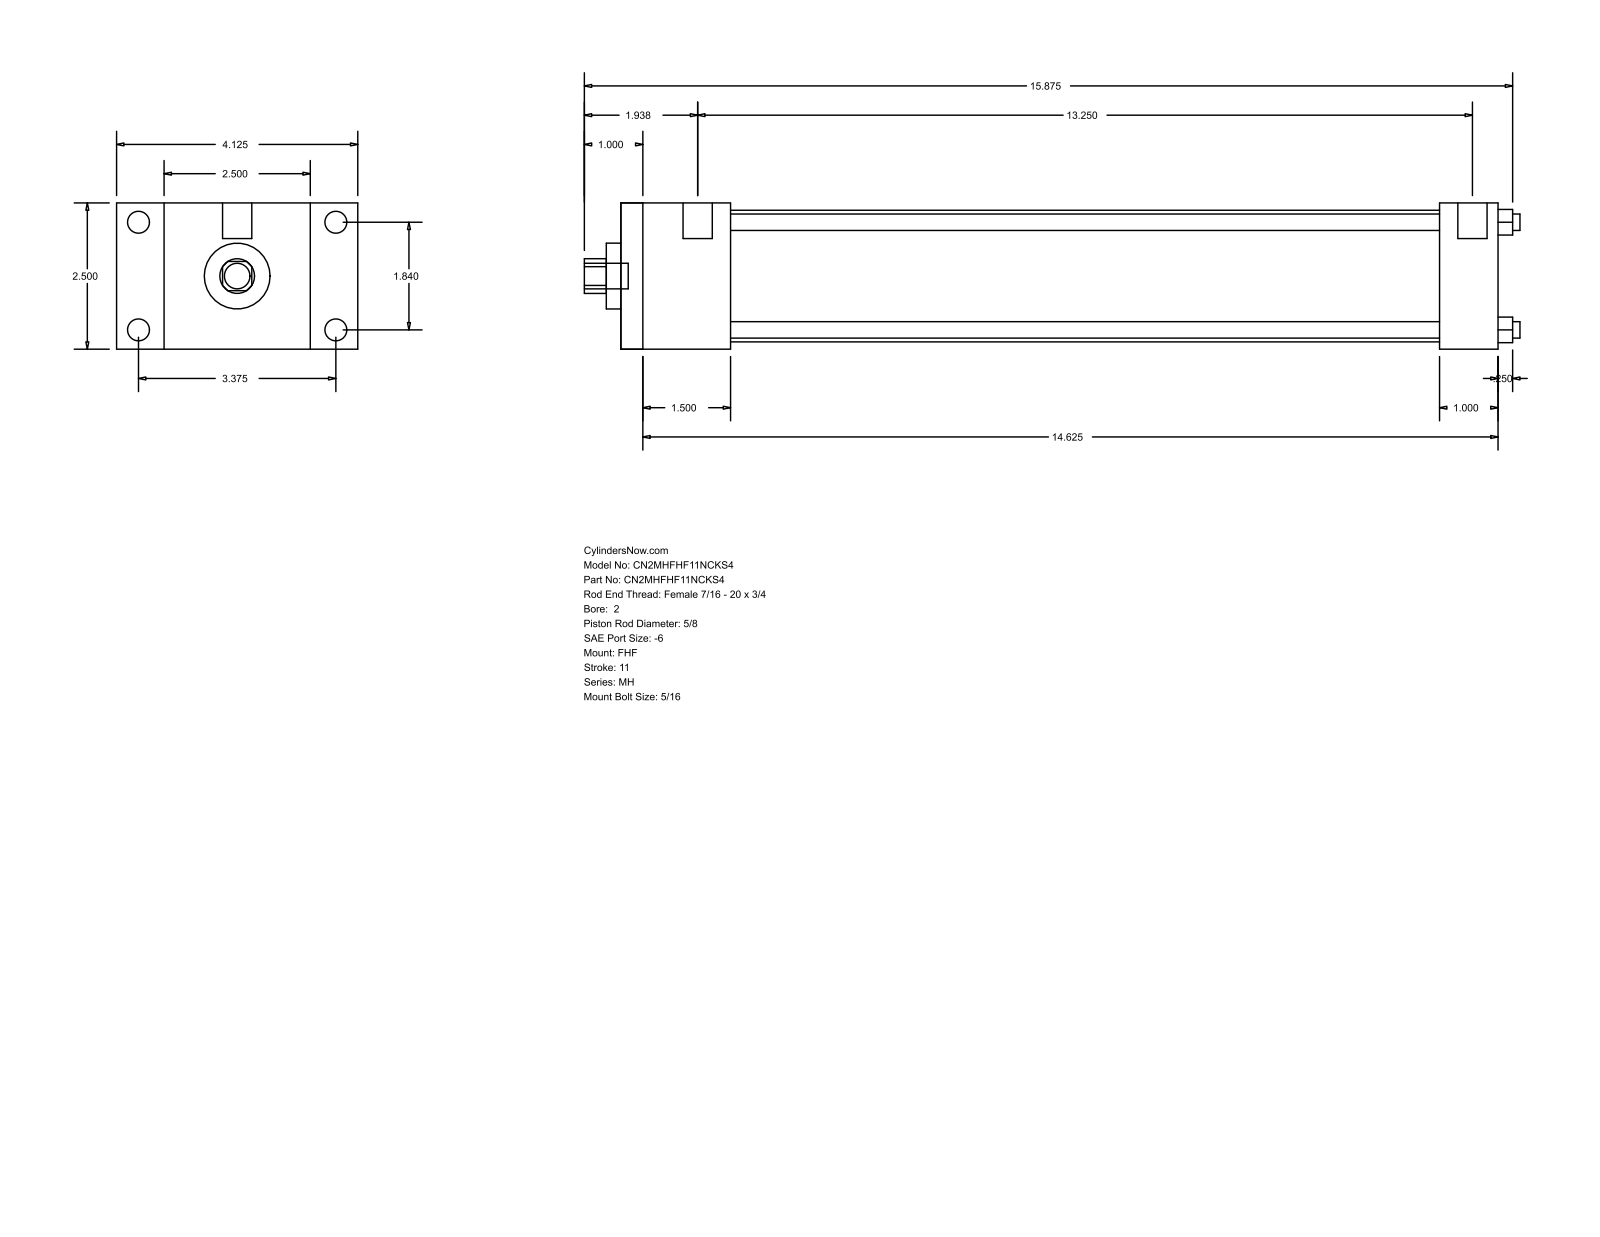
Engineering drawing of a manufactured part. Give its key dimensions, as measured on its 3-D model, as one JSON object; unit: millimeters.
{"part_name": "MH_FHF__0200_0.625", "step_written_by": "GSSL Pune (CONFIG_CONTROL_DESIGN)", "units": "millimeters", "bodies": {"solids": 0, "faces": 88, "planar": 60, "cylindrical": 28, "other": 0}, "overall_size": [406.4, 104.78, 63.5], "round_holes": [[7.14, 4], [15.88, 1], [28.57, 1], [57.15, 1]], "round_bosses_or_shafts": [[9.53, 4], [5.56, 4], [12.7, 2], [11.11, 1]], "partial_cylinders_radius": [[7.54, 1]], "face_to_face_distances": [63.5, 47.62, 381, 333.38, 20.64, 84.14, 104.78, 25.4, 355.6, 307.98], "hole_center_spacings": [33.05, 46.74, 66.1]}
